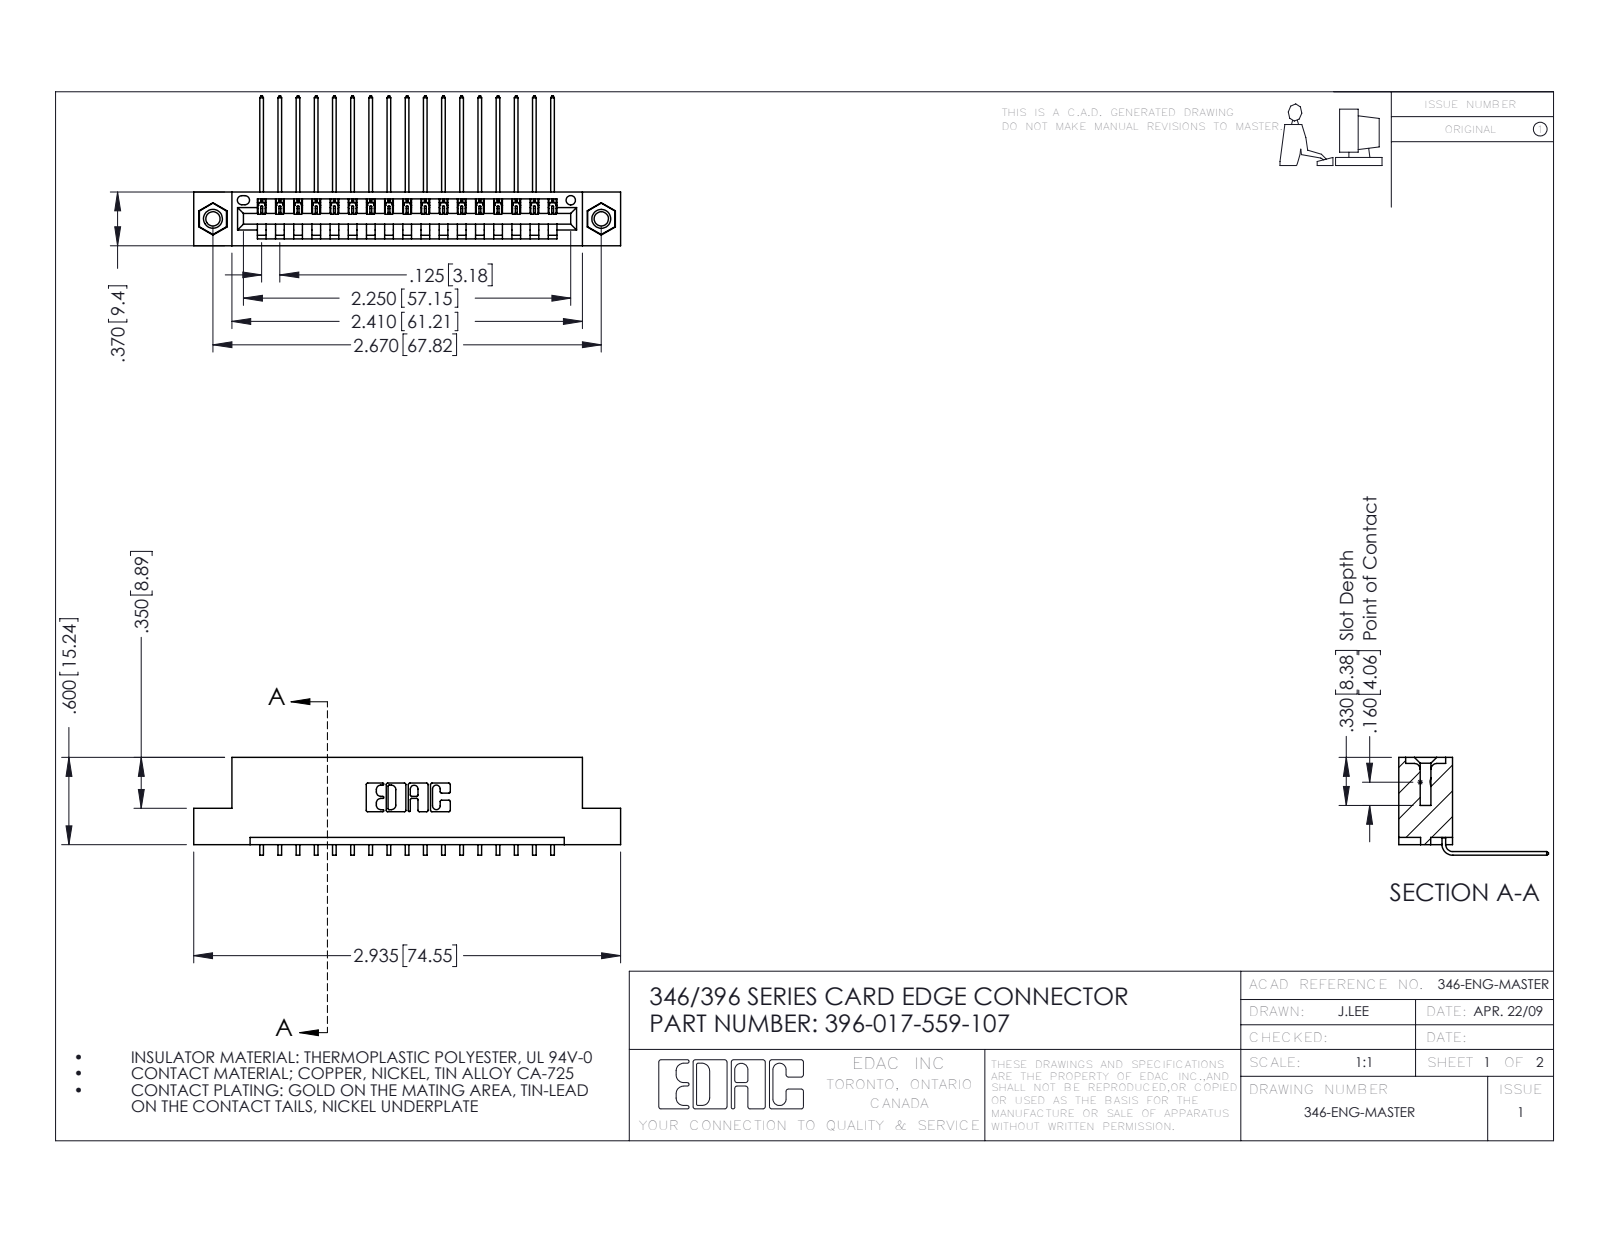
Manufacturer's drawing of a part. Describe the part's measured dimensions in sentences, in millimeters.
The part is named "345-250-001_345-250-005-103; 345-292-001_558 559 Tail - 1; 396-017-559-107; 346 Part_Flush Mounting Lugs - 0.156 Dia-TI". Its 3-D file was written by "SolidWorks 2016 (CONFIG_CONTROL_DESIGN)". It is 20 solids with 1202 faces: 822 planar, 364 cylindrical and 16 other. Overall it measures 74.5 by 26.2 by 17.1 millimeters. Its volume is 7 010 cubic millimeters and its surface area 8 858 square millimeters. Round holes: 2 of diameter 2.5, 2 of diameter 3.2, 2 of diameter 4, 1 of diameter 1.6. Round bosses or shafts: 2 of diameter 3.9. Partial cylindrical surfaces (rounded edges, fillets, slot ends): 34 of radius 0.2, 22 of radius 0.3, 6 of radius 0.2, 6 of radius 0.8, 3 of radius 0.7, 2 of radius 0.8, 2 of radius 1, 1 of radius 0.4. The main face-to-face distances are 1.2, 8.2, 9.4, 6.4, 1.8, 0.6, 7.6, 3.8, 5.6, 2.5. The hole center spacings are 6.2, 62.6, 67.8.
